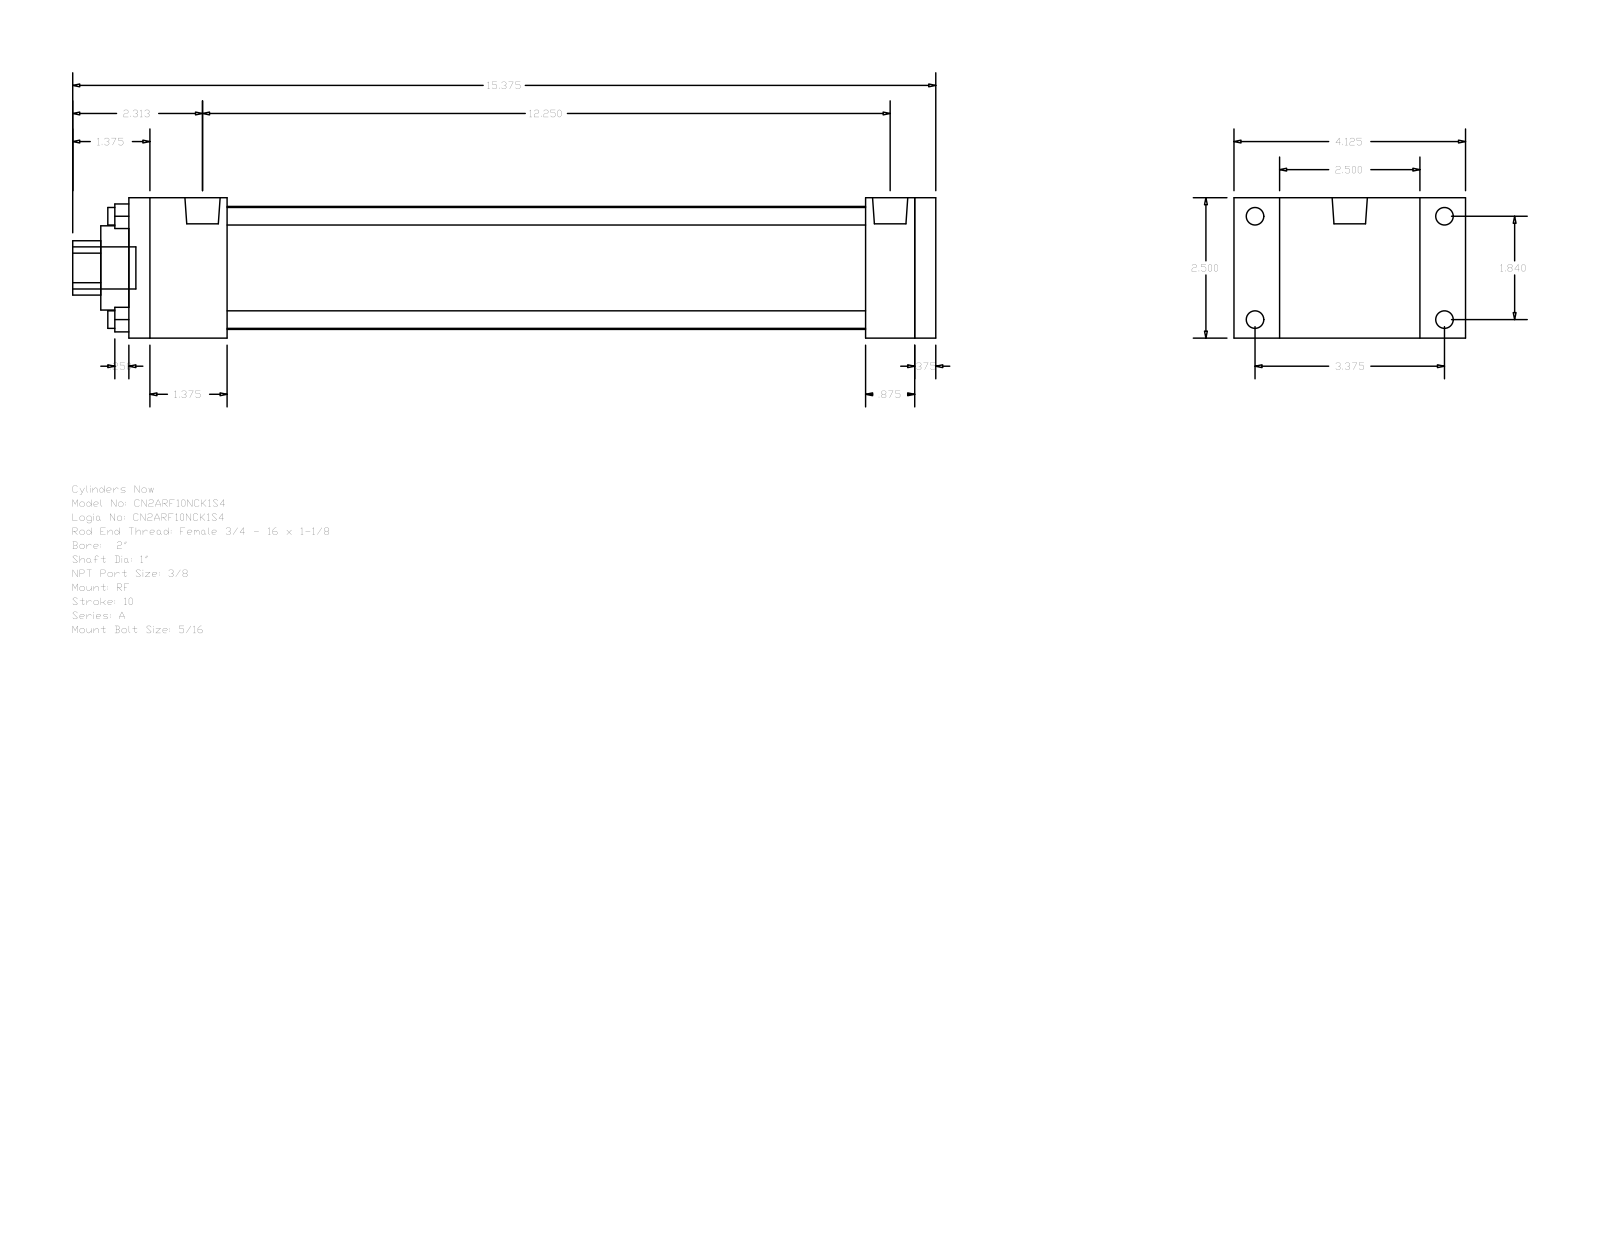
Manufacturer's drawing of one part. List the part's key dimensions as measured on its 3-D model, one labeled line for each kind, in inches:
Part name (STEP PRODUCT): A_RF__0200_1
STEP written by: GSSL Pune (CONFIG_CONTROL_DESIGN)
Units: inches
Bodies: 0 solids, 92 faces (64 planar, 28 cylindrical, 0 other)
Overall size (bounding box): 15.375 × 4.125 × 2.5
Round holes (diameter × count): ⌀0.313 ×4, ⌀1 ×1, ⌀1.5 ×1, ⌀2.19 ×1
Round bosses / shafts (diameter × count): ⌀0.313 ×4, ⌀0.219 ×4, ⌀0.627 ×2, ⌀0.75 ×1
Partial cylindrical surfaces — rounded edges, fillets, slot ends (radius × count): R0.484 ×1
Main face-to-face distances: 2.5, 0.375, 14.375, 14, 0.813, 1.75, 12.25, 12.625, 13.125, 11.375
Hole centre spacings: 1.301, 1.84, 2.602
